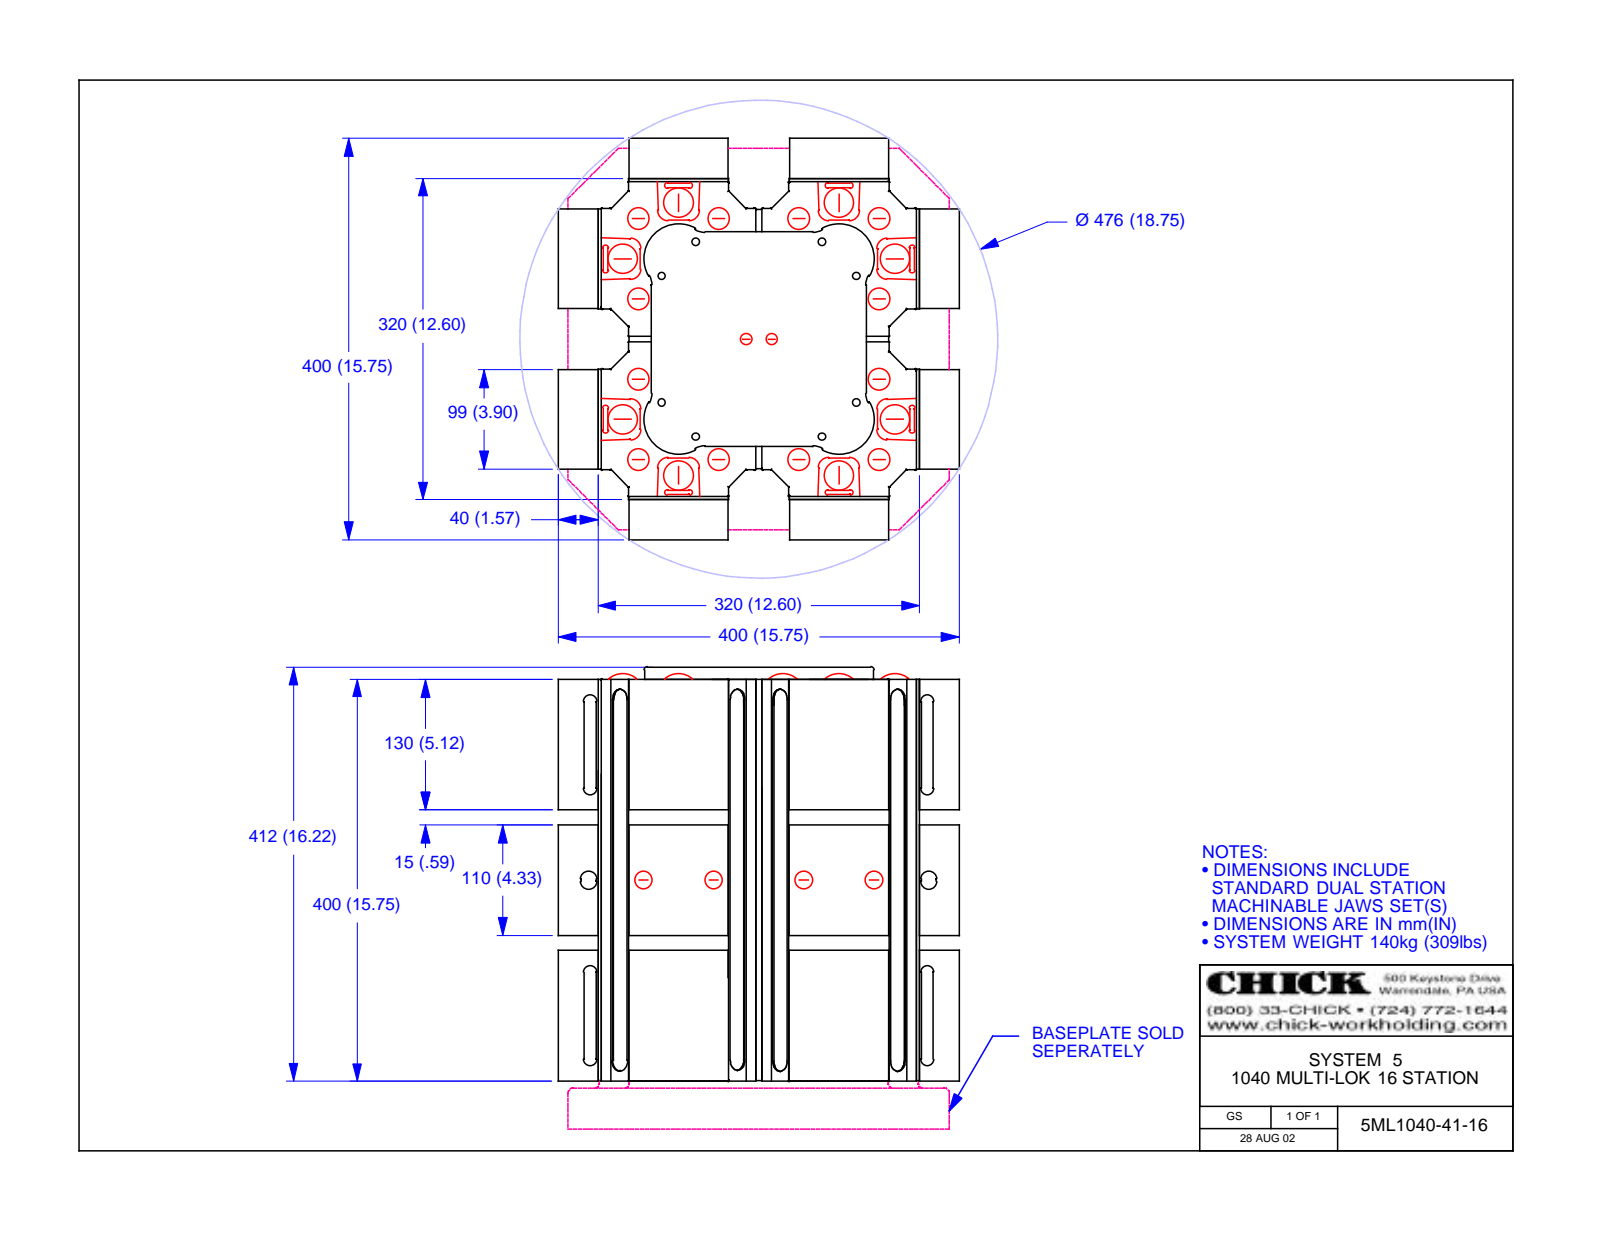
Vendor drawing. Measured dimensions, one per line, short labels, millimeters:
name: 5ML1040-41-16; 5CLM1040-41-16; 5DS1040-10-40; 5FJ1040-10-40 (+2 more)
written by: Autodesk Inventor 2013 (AUTOMOTIVE_DESIGN)
unit: mm
bodies: 33 solids, 6510 faces (3532 planar, 1096 cylindrical, 1882 other)
size: 405.5 × 399.32 × 399.32
volume: 43 400 000 mm³; area: 2 962 000 mm²
holes: 32× ⌀10.11, 30× ⌀6.65, 30× ⌀9, 30× ⌀14.15, 30× ⌀19.34, 22× ⌀12.7, 20× ⌀10, 16× ⌀4.92, 16× ⌀8.65, 16× ⌀20, 12× ⌀4.06, 12× ⌀6.87
bosses: 16× ⌀8.4, 12× ⌀7.67, 12× ⌀4.76
rounds: 142× R1.5, 48× R0.4, 48× R1.2, 38× R4.8, 35× R11.1, 24× R1.65, 24× R2.83, 24× R7
face distances: 3, 316.93, 159.93, 39.7, 42.7, 356.63, 359.63, 313.93, 319.93, 64.99
hole spacings: 113.09, 150, 165.53, 159.93, 70, 226.17, 185, 197.8
